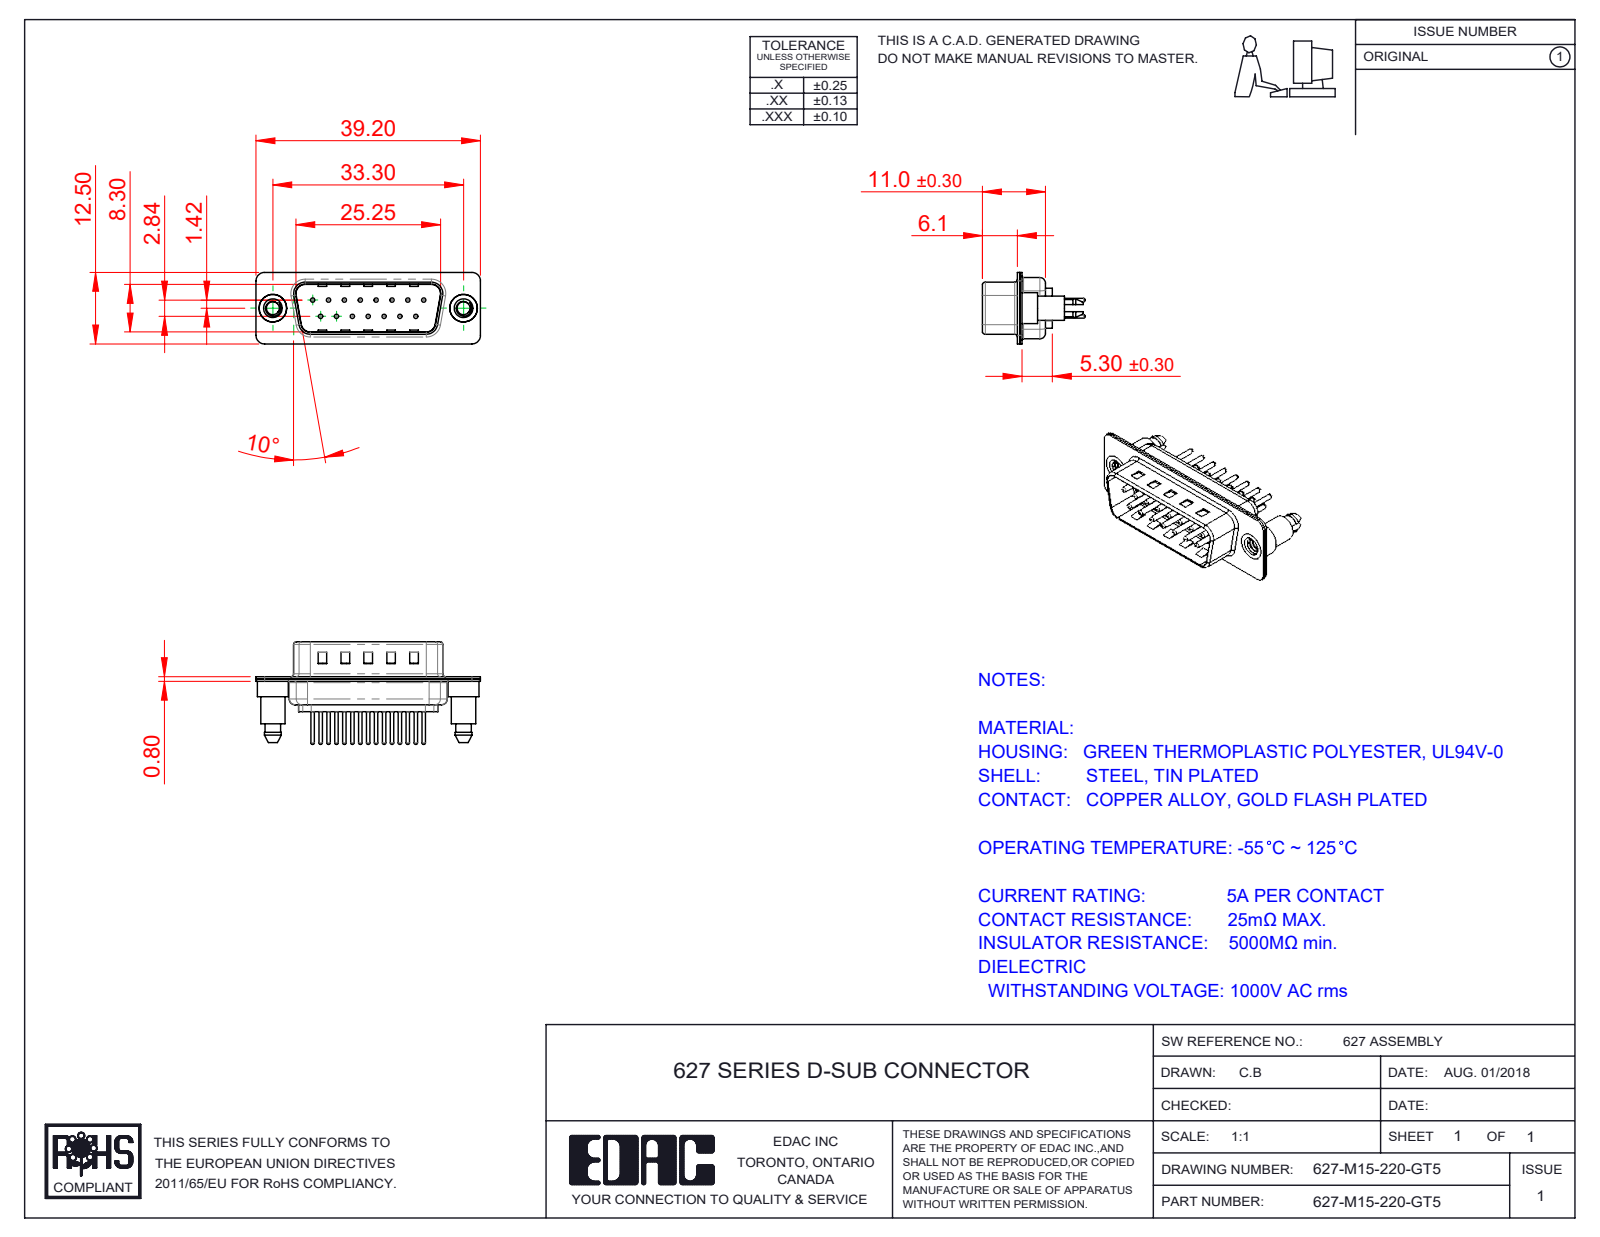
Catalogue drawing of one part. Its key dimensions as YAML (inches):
part_name: "627-M15-220-GT5; 627M Shell Rear_15 Contacts; 627M 4-40 Threaded Boardlock; 627M Housing_15 Contacts (+3 more)"
step_written_by: "SolidWorks 2020 (CONFIG_CONTROL_DESIGN)"
units: inches
bodies: {solids: 20, faces: 945, planar: 260, cylindrical: 375, other: 310}
overall_size: [1.543, 0.705, 0.492]
volume: 0.121
surface_area: 7.969
round_holes:
  - {diameter: 0.03, count: 15}
  - {diameter: 0.063, count: 15}
  - {diameter: 0.079, count: 15}
  - {diameter: 0.089, count: 2}
  - {diameter: 0.157, count: 2}
  - {diameter: 0.189, count: 2}
round_bosses_or_shafts:
  - {diameter: 0.059, count: 15}
  - {diameter: 0.024, count: 15}
  - {diameter: 0.213, count: 2}
  - {diameter: 0.193, count: 2}
  - {diameter: 0.167, count: 2}
partial_cylinders:
  - {radius: 0.059, count: 18}
  - {radius: 0.079, count: 12}
  - {radius: 0.063, count: 10}
  - {radius: 0.02, count: 8}
  - {radius: 0.01, count: 4}
  - {radius: 0.024, count: 4}
  - {radius: 0.026, count: 4}
  - {radius: 0.035, count: 4}
face_to_face_distances: [0.016, 0.031, 0.374, 0.358, 0.343, 0.39, 0.209, 0.047, 0.24, 0.224]
hole_center_spacings: [0.124, 0.109, 0.218, 0.327, 0.436, 0.198, 0.198, 0.294]
